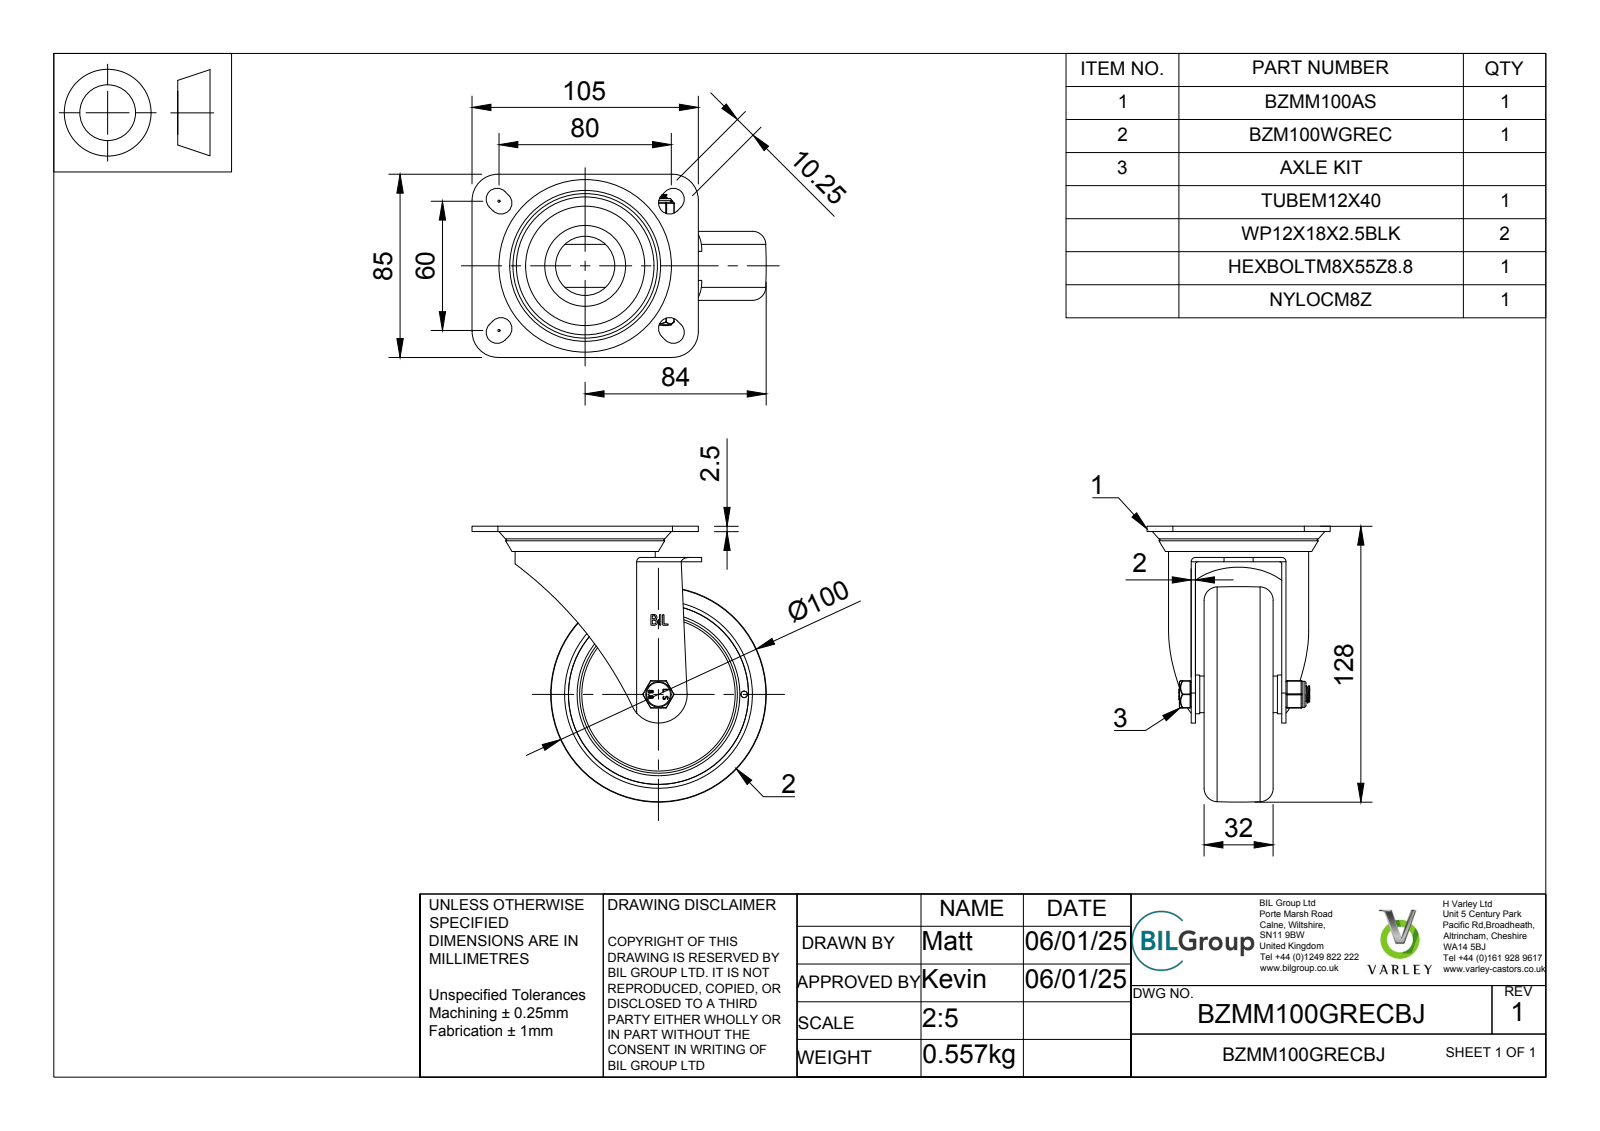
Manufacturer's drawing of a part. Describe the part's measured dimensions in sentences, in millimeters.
The part is named "BZMM100GREC v3; BZMM100AS - 2 v2; ZINC PLATED, PRESSED STEEL TOP PLATE; ZINC PLATED, PRESSED STEEL TOP PLATE Geometry (+7 more)". Its 3-D file was written by "Autodesk Translation Framework v13.20.0.188 (AP242_MANAGED_MODEL_BASED_3D_ENGINEERING_MIM_LF)". It is 36 solids with 389 faces: 128 planar, 141 cylindrical and 120 other. Overall it measures 136.5 by 128 by 85 millimeters. Its volume is 197 254 cubic millimeters and its surface area 106 662 square millimeters. Round holes: 2 of diameter 0.66, 1 of diameter 3, 1 of diameter 8, 1 of diameter 8.25, 1 of diameter 8.4, 1 of diameter 8.6, 1 of diameter 10.1, 1 of diameter 12.4, 1 of diameter 27.5, 1 of diameter 48, 1 of diameter 61, 1 of diameter 83.5. Round bosses or shafts: 1 of diameter 65, 1 of diameter 31.5, 1 of diameter 18, 1 of diameter 17, 1 of diameter 12.1, 1 of diameter 11.9, 1 of diameter 11.5, 1 of diameter 7.87. Partial cylindrical surfaces (rounded edges, fillets, slot ends): 18 of radius 0.5, 12 of radius 0.25, 8 of radius 5.12, 4 of radius 0.33, 4 of radius 0.64, 4 of radius 1, 4 of radius 12, 2 of radius 0.63. The main face-to-face distances are 2, 6, 19, 13, 2.5, 38, 4, 42, 36, 25. The hole center spacings are 3.22, 42.74, 2.49, 39.75.
